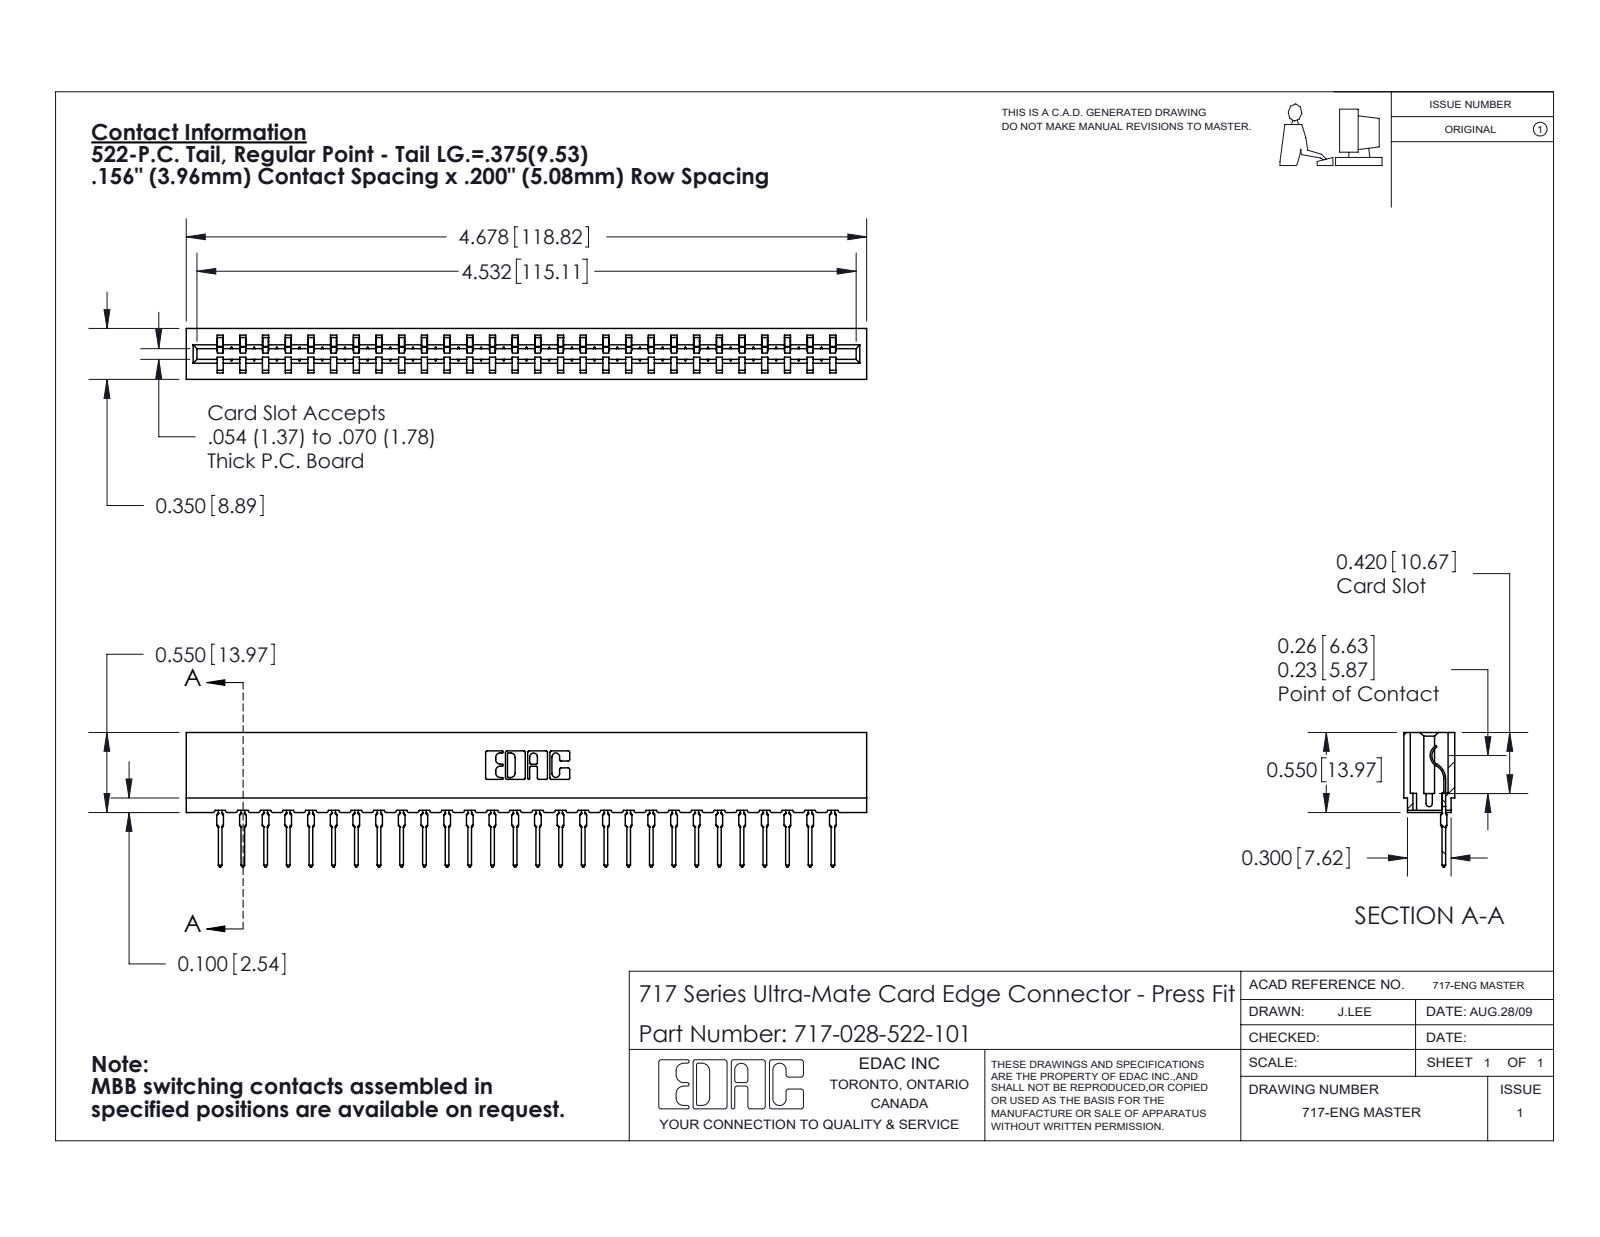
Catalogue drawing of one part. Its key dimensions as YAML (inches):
part_name: "745-292-001_522; 717-028-522-101; 717 Part_Insulator Option - 06"
step_written_by: "SolidWorks 2020 (CONFIG_CONTROL_DESIGN)"
units: inches
bodies: {solids: 29, faces: 3258, planar: 1958, cylindrical: 572, other: 728}
overall_size: [4.678, 0.924, 0.35]
volume: 0.617
surface_area: 21.87
partial_cylinders:
  - {radius: 0.015, count: 56}
  - {radius: 0.021, count: 56}
  - {radius: 0.01, count: 22}
  - {radius: 0.007, count: 6}
  - {radius: 0.031, count: 6}
  - {radius: 0.005, count: 4}
  - {radius: 0.011, count: 4}
  - {radius: 0.026, count: 3}
face_to_face_distances: [0.212, 0.138, 0.35, 0.074, 0.156, 0.045, 0.305, 0.093, 0.167, 0.063]
